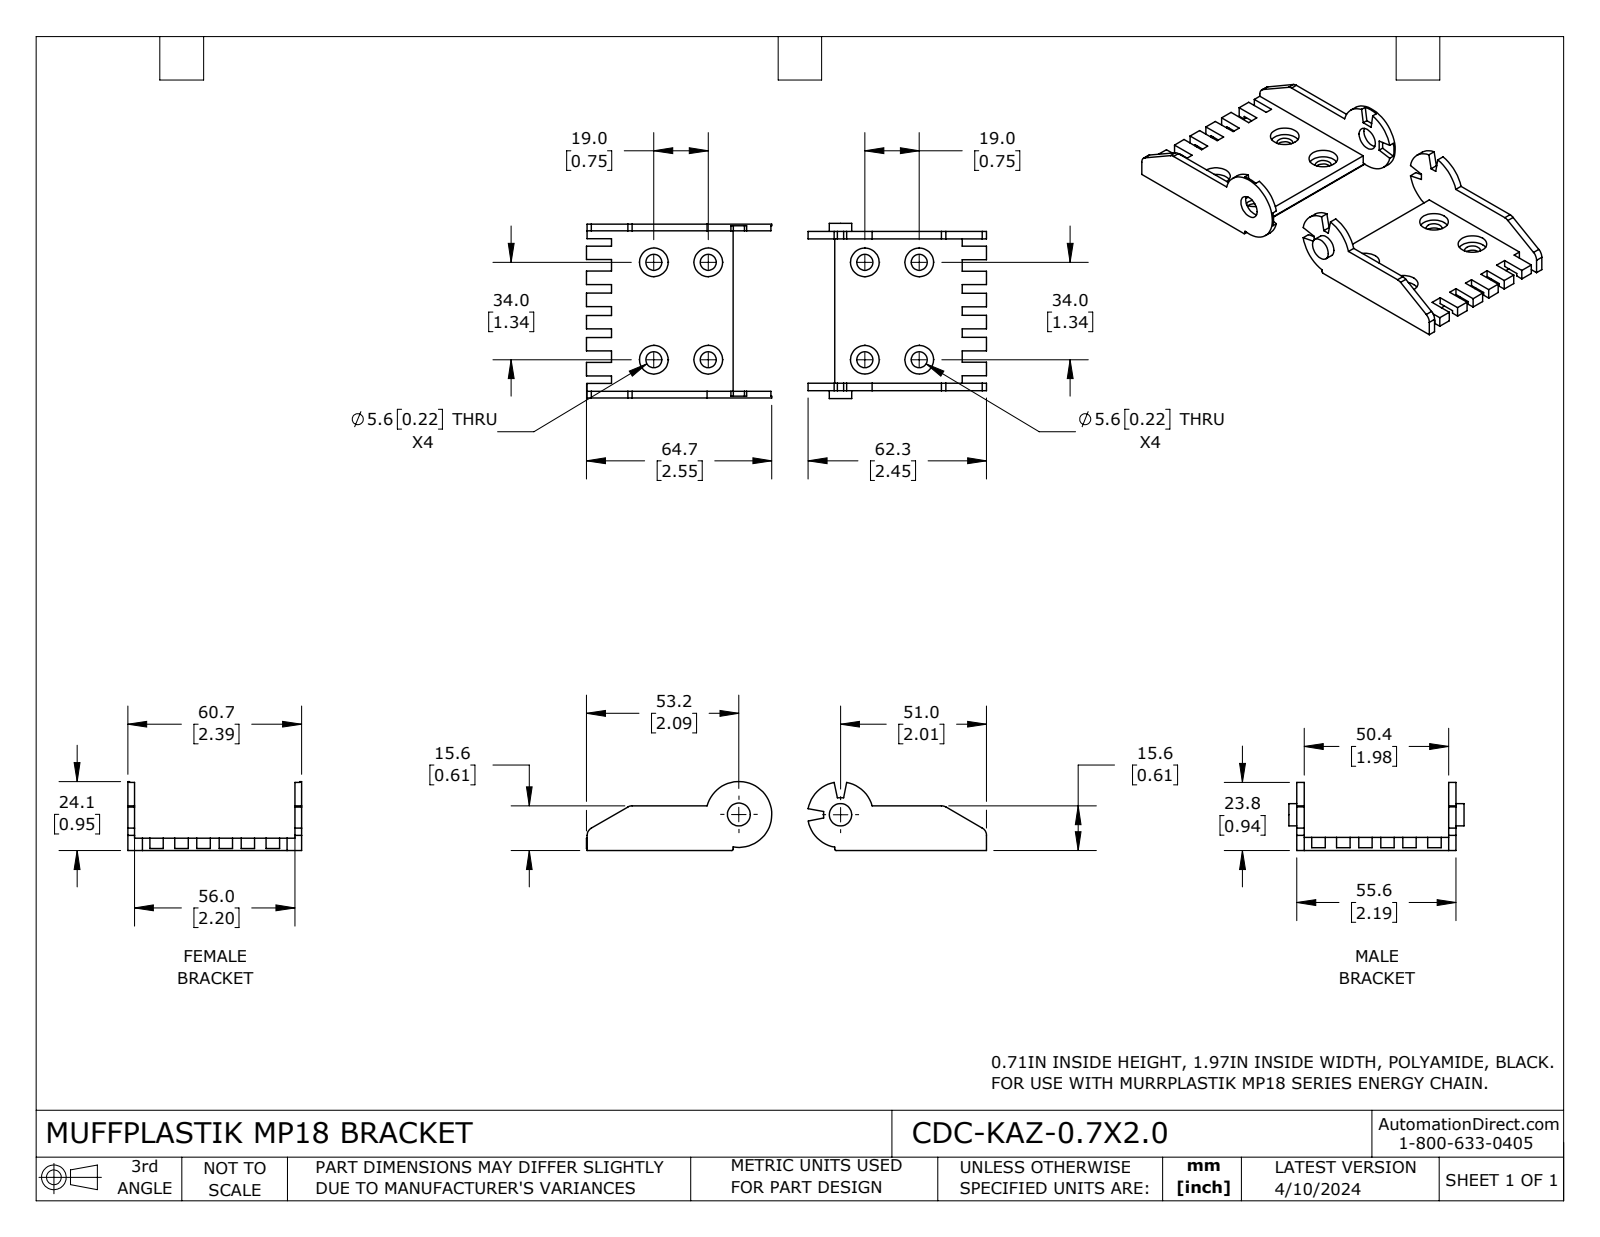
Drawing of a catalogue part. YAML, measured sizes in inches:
part_name: "CDC-KAZ-0.7X2.0_Female; CDC-KAZ-0.7X2.0_Male; CDC-KAZ-0.7X2.0"
step_written_by: "SolidWorks 2023 (CONFIG_CONTROL_DESIGN)"
units: inches
bodies: {solids: 2, faces: 200, planar: 140, cylindrical: 60, other: 0}
overall_size: [5.5, 2.409, 0.949]
volume: 1.819
surface_area: 33.29
round_holes:
  - {diameter: 0.22, count: 8}
  - {diameter: 0.394, count: 8}
  - {diameter: 0.315, count: 1}
round_bosses_or_shafts:
  - {diameter: 0.307, count: 1}
partial_cylinders:
  - {radius: 0.118, count: 4}
  - {radius: 0.02, count: 2}
  - {radius: 0.453, count: 2}
face_to_face_distances: [0.169, 0.181, 0.11, 0.1, 2.289, 2.087, 0.102, 0.203, 2.187, 2.197]
hole_center_spacings: [0.748, 1.339, 1.533, 2.902, 3.195, 2.154, 2.536, 3.65]
